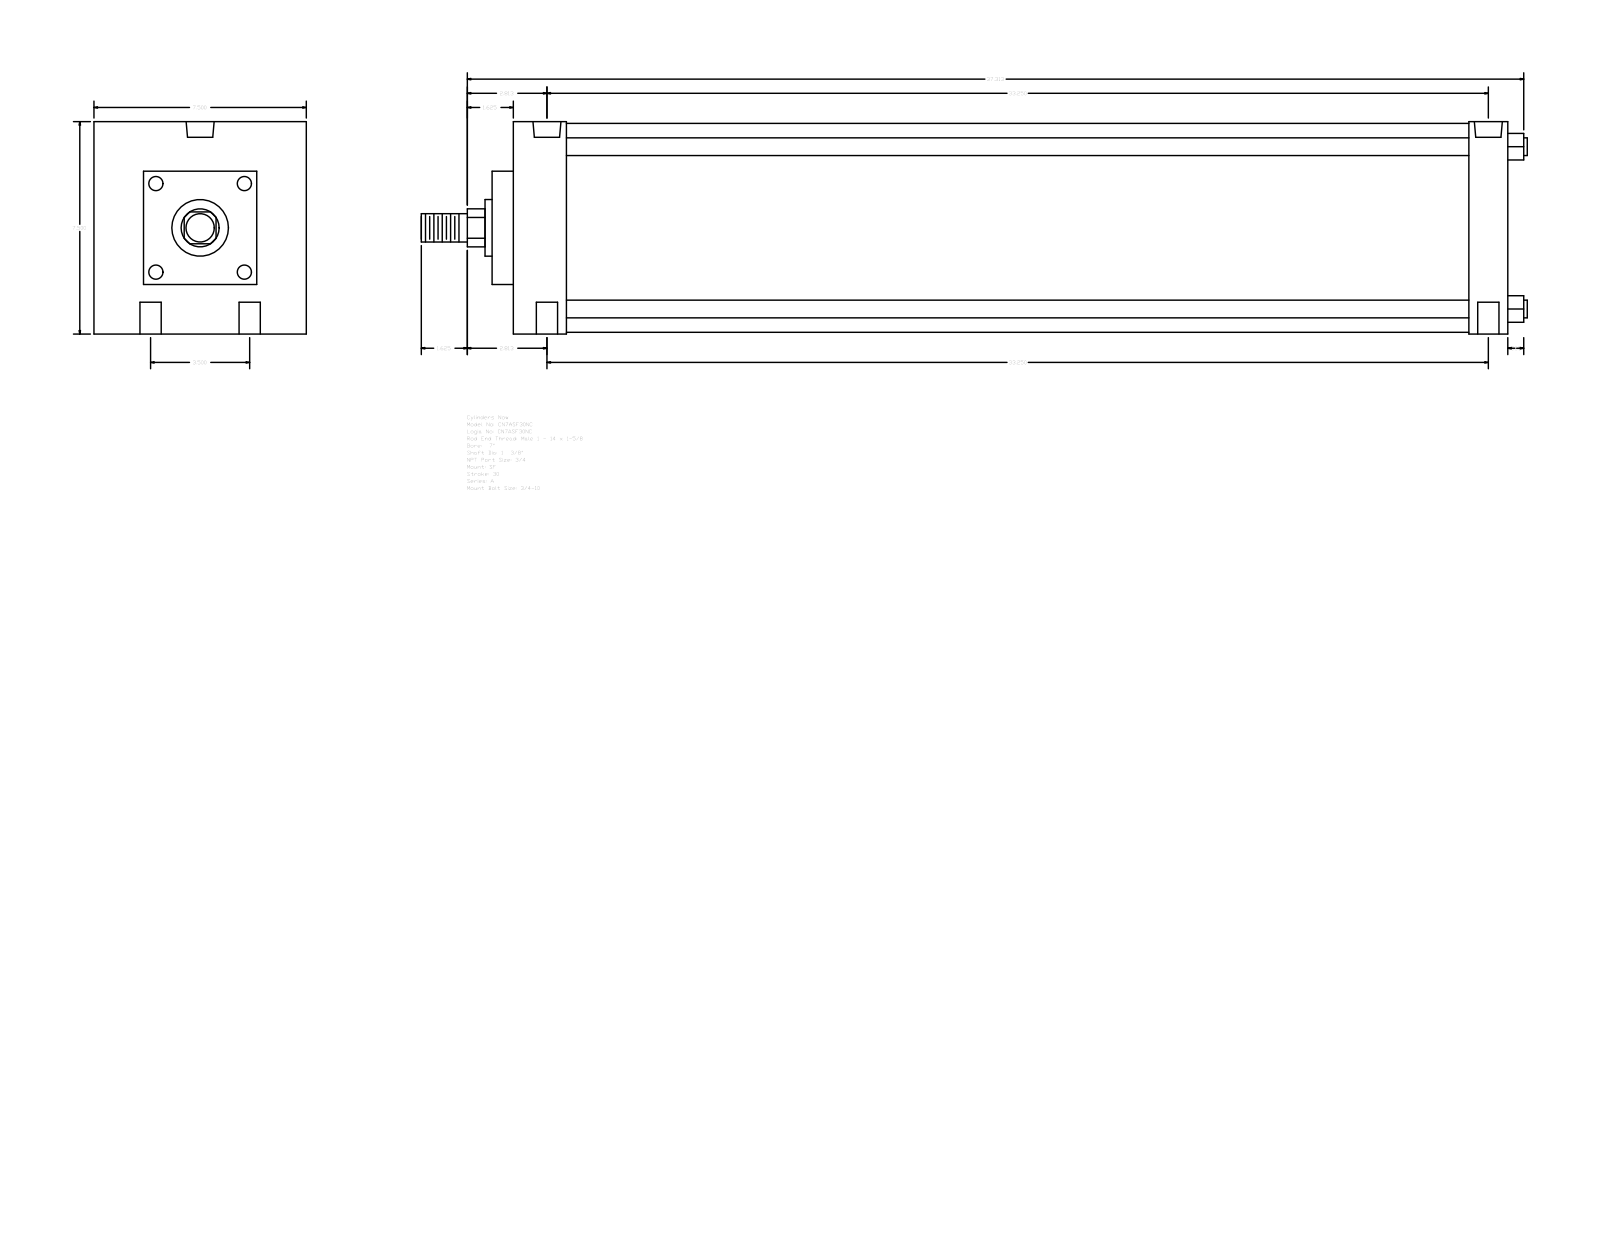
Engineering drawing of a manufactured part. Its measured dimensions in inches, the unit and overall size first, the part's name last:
Units: inches
Overall size (bounding box): 39.063 × 7.5 × 7.5
Round holes (diameter × count): ⌀0.75 ×4, ⌀0.594 ×2, ⌀0.989 ×2
Round bosses / shafts (diameter × count): ⌀0.625 ×4, ⌀7.375 ×1, ⌀2 ×1, ⌀1.375 ×1, ⌀1 ×1
Partial cylindrical surfaces — rounded edges, fillets, slot ends (radius × count): R0.672 ×1
Main face-to-face distances: 7.5, 35.125, 0.75, 35.875, 2.625, 34.5, 1.875, 33.75, 31.875, 33.25
Hole centre spacings: 1.75, 33.296, 33.25, 3.5, 33.434, 32.812
Bodies: 0 solids, 93 faces (67 planar, 26 cylindrical, 0 other)
Part name (STEP PRODUCT): A_SF__0700_1.375
STEP written by: GSSL Pune (CONFIG_CONTROL_DESIGN)
